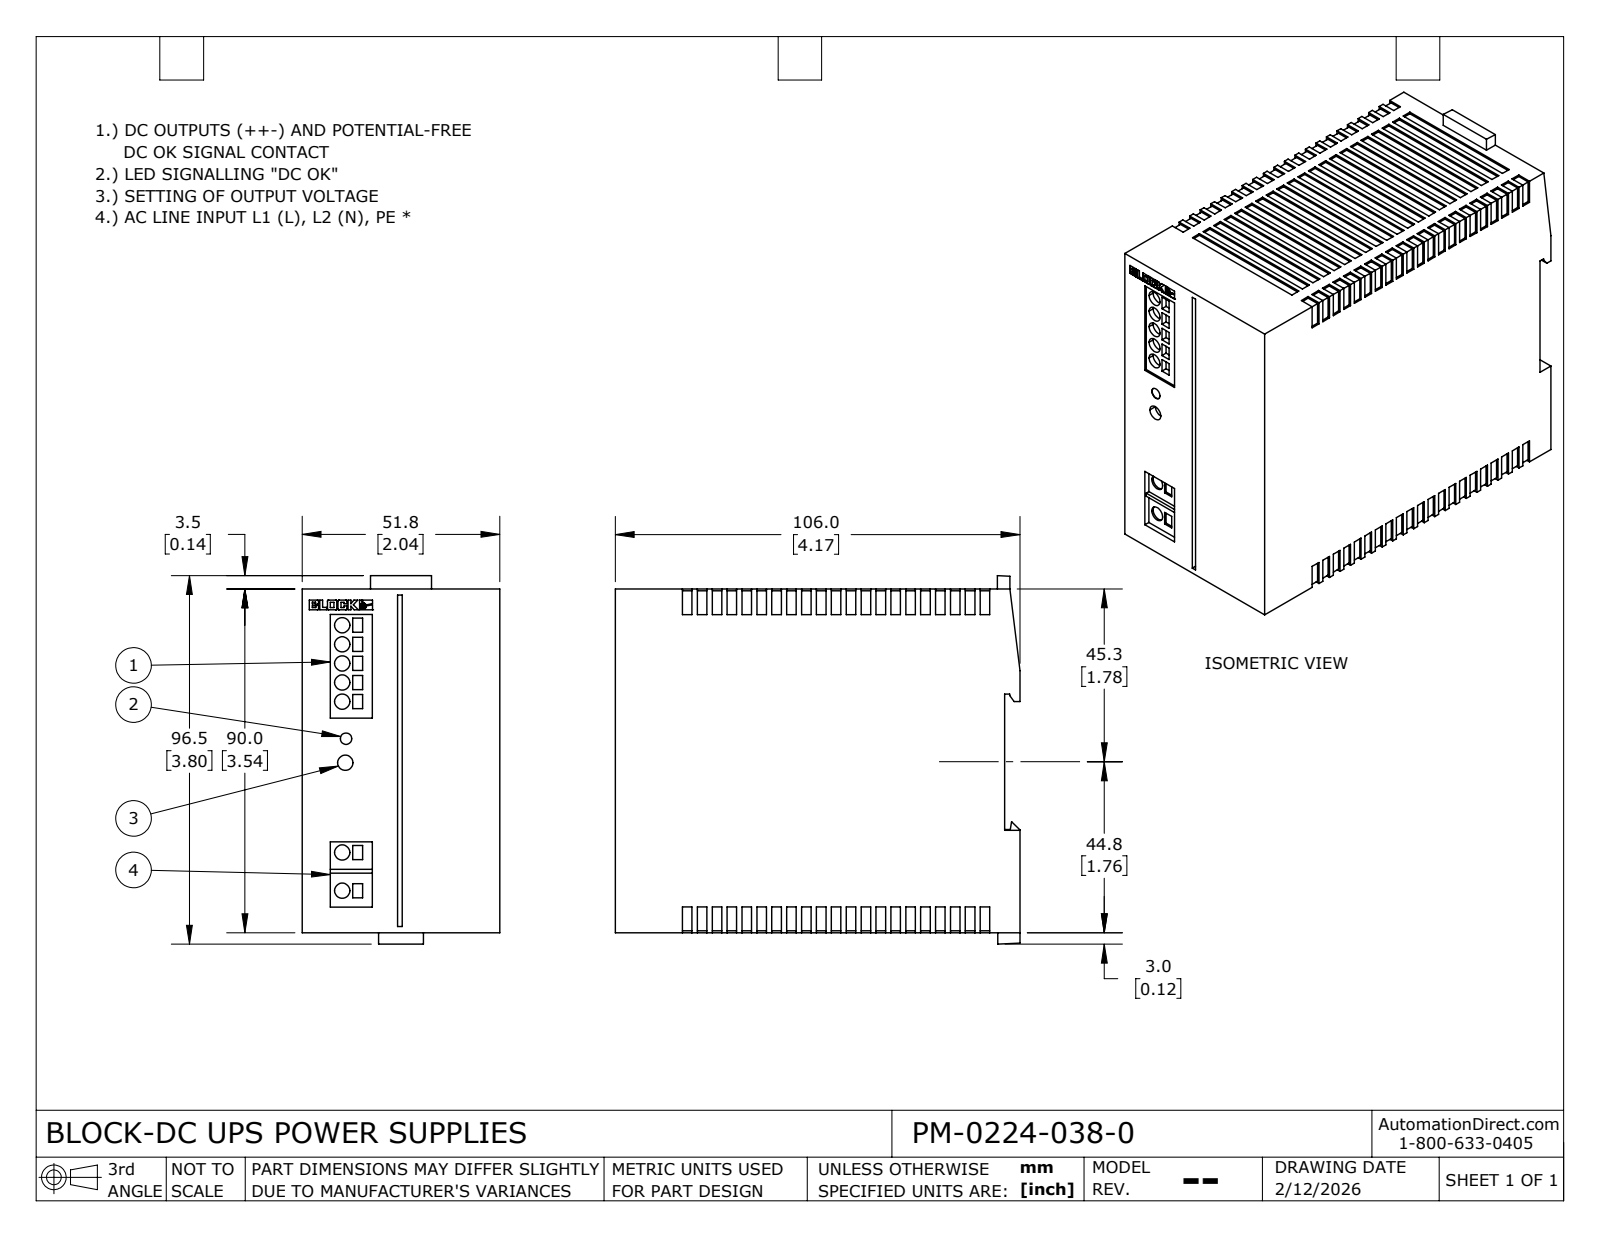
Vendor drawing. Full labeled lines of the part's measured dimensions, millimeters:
Part name (STEP PRODUCT): PM-0224-038-0_Default
STEP written by: SolidWorks 2024 (CONFIG_CONTROL_DESIGN)
Units: millimetres
Bodies: 1 solid, 1020 faces (1000 planar, 20 cylindrical, 0 other)
Overall size (bounding box): 106 × 96.5 × 51.8
Volume: 481 999 mm³ · Surface area: 42 960 mm²
Round holes (diameter × count): ⌀4 ×8, ⌀0.96 ×1, ⌀3 ×1
Main face-to-face distances: 51.8, 0.5, 89.5, 90, 89, 4, 102, 106, 51.3, 3.9
Hole centre spacings: 5, 10, 15, 49.5, 54.5, 59.5, 6.3, 7.46
